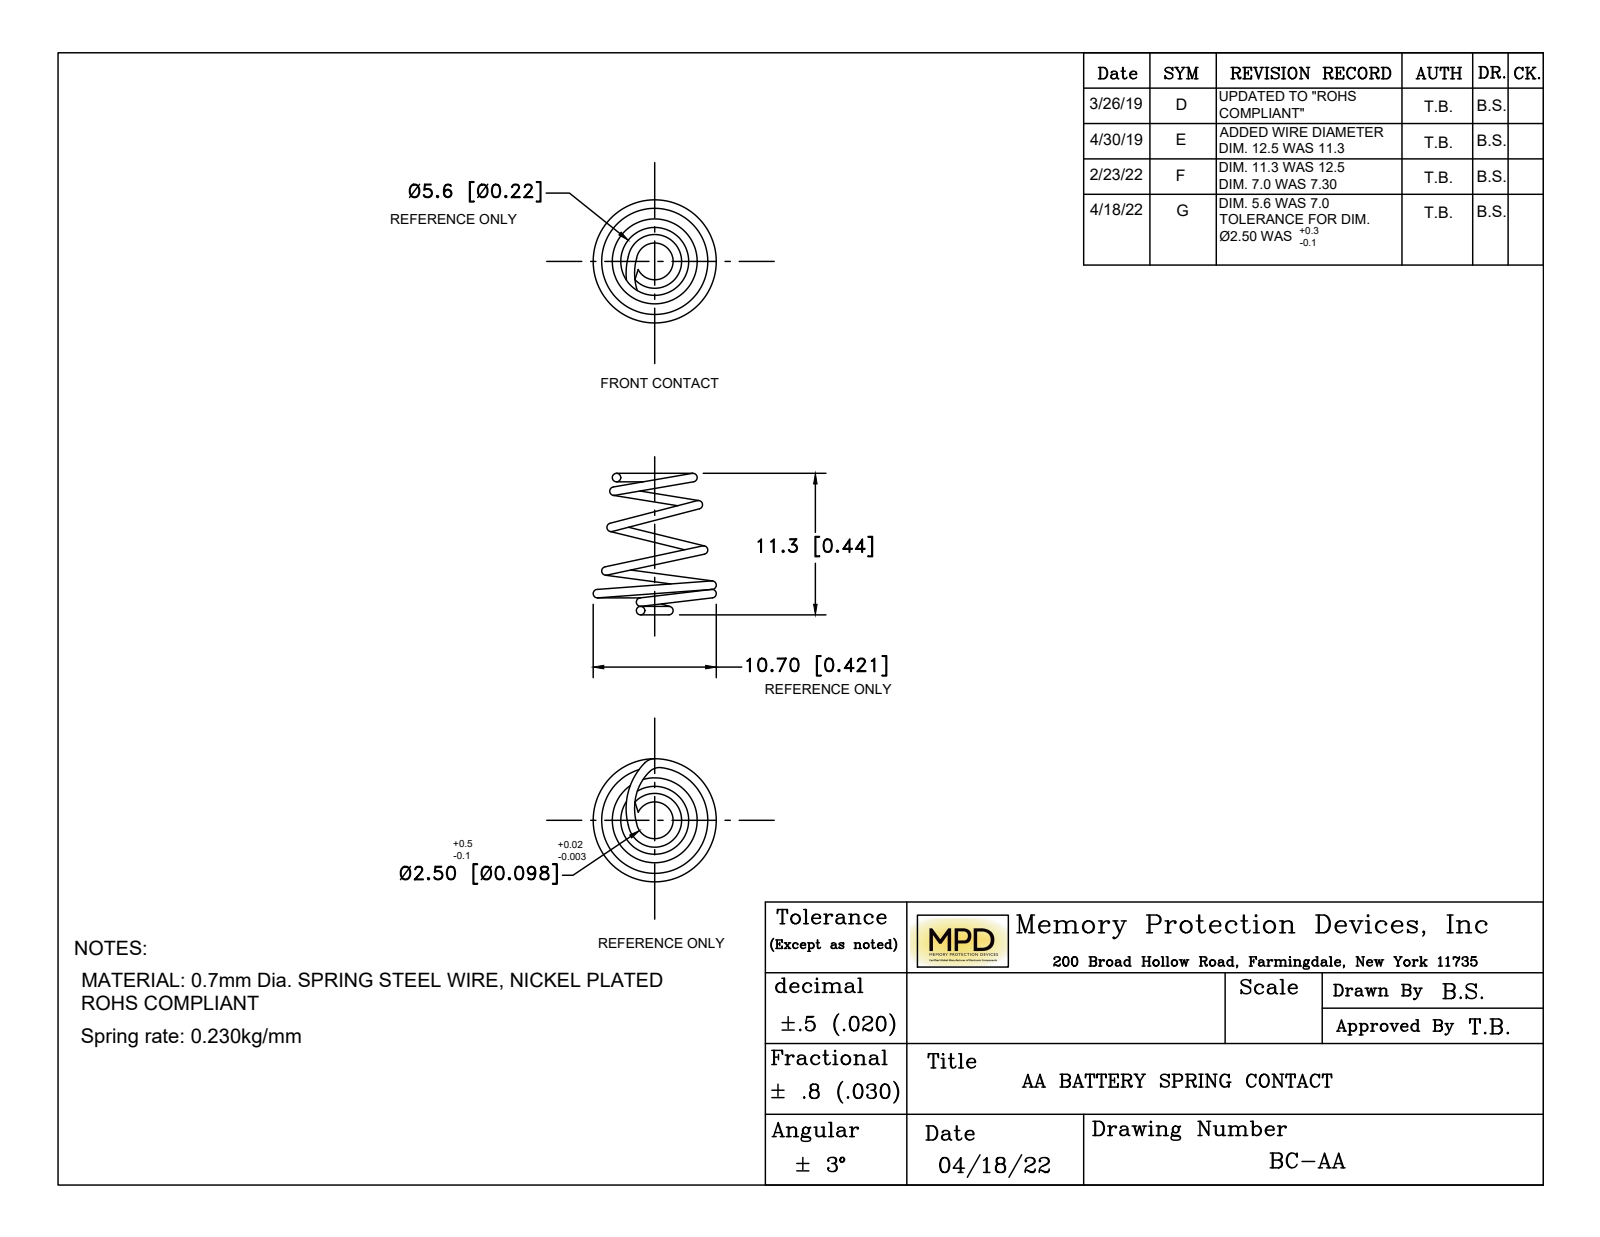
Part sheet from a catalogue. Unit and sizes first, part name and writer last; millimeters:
Units: millimetres
Overall size (bounding box): 12.5 × 10.7 × 10.7
Volume: 49 mm³ · Surface area: 279 mm²
Bodies: 1 solid, 11 faces (3 planar, 0 cylindrical, 8 other)
Part name (STEP PRODUCT): BCAA
STEP written by: SolidWorks 2017 (AUTOMOTIVE_DESIGN)
